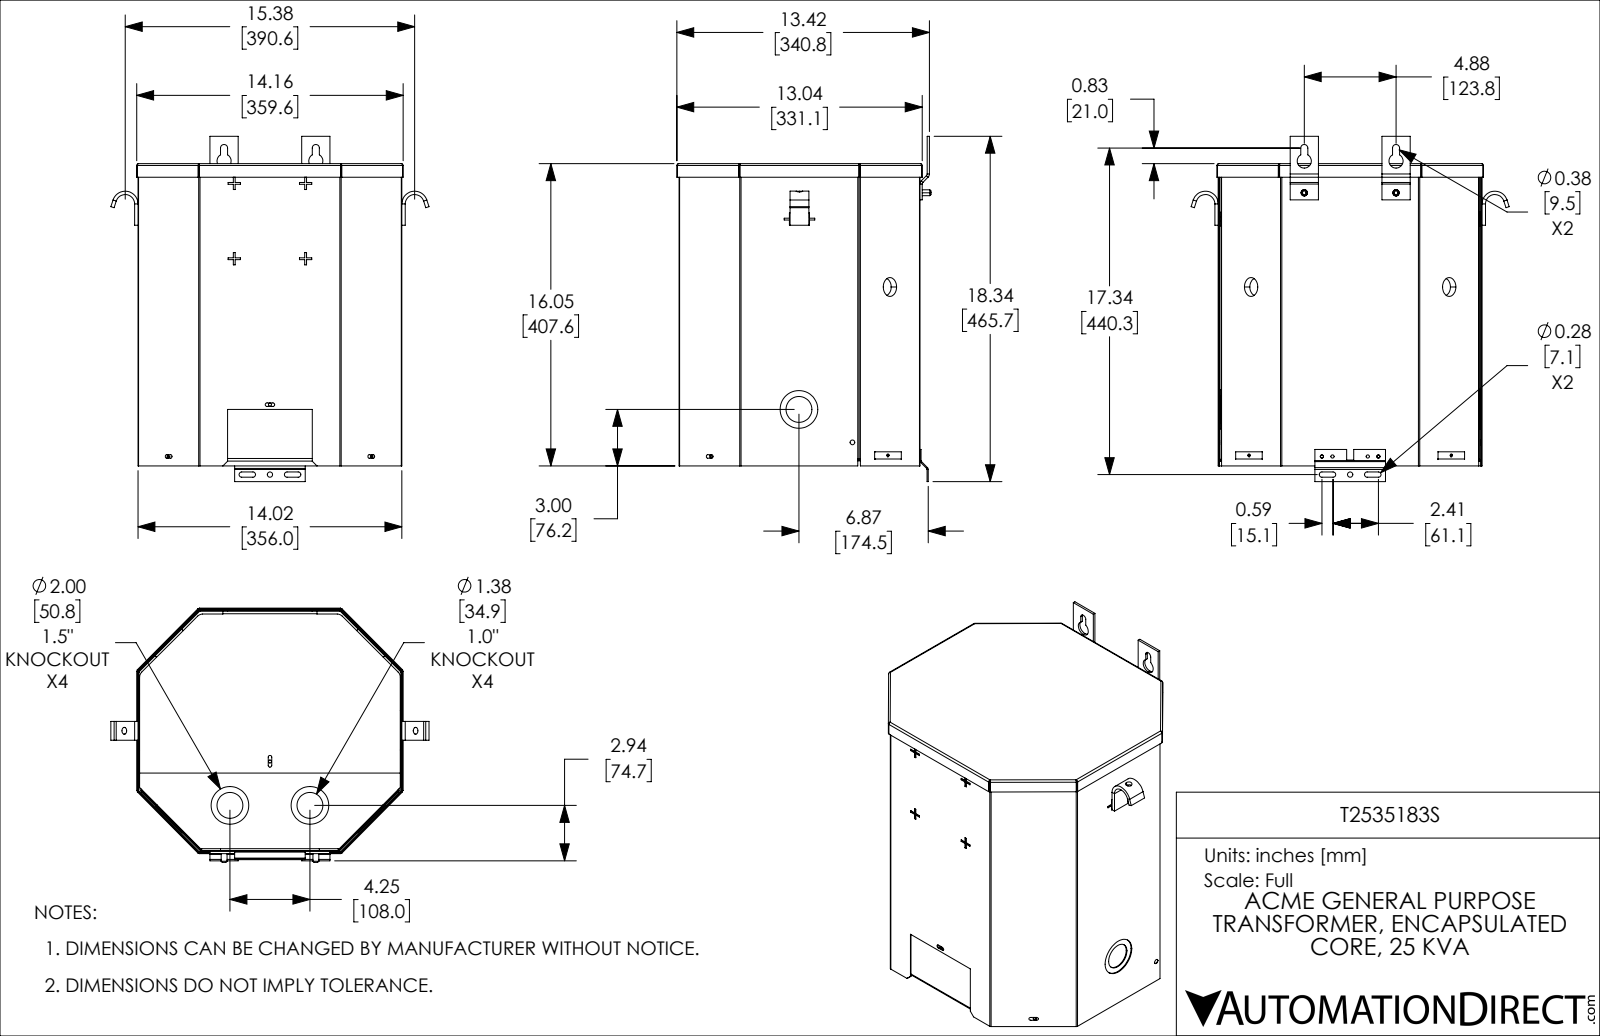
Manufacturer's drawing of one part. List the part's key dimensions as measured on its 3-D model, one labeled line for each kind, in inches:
Part name (STEP PRODUCT): T2535183S
STEP written by: SolidWorks 2021 (CONFIG_CONTROL_DESIGN)
Units: inches
Bodies: 13 solids, 764 faces (528 planar, 200 cylindrical, 36 other)
Overall size (bounding box): 18.335 × 16.899 × 13.499
Volume: 60.45 in³ · Surface area: 2 359 in²
Round holes (diameter × count): ⌀0.159 ×5, ⌀0.171 ×4, ⌀0.16 ×3, ⌀1.375 ×3, ⌀2 ×3, ⌀0.25 ×2, ⌀0.256 ×2, ⌀0.281 ×2, ⌀0.313 ×2, ⌀0.344 ×2, ⌀0.75 ×2
Round bosses / shafts (diameter × count): ⌀2.12 ×2, ⌀1.494 ×2, ⌀0.312 ×2, ⌀2.096 ×1, ⌀1.47 ×1
Partial cylindrical surfaces — rounded edges, fillets, slot ends (radius × count): R0.05 ×19, R0.098 ×19, R0.094 ×16, R0.075 ×5, R0.135 ×5, R0.141 ×4, R0.375 ×4, R0.125 ×2
Main face-to-face distances: 0.048, 12.75, 13.969, 0.048, 14.248, 14.296, 14.2, 14.248, 0.06, 12.702
Hole centre spacings: 0.563, 1.342, 1.688, 1.781, 2.437, 2.906, 3.133, 3.152
